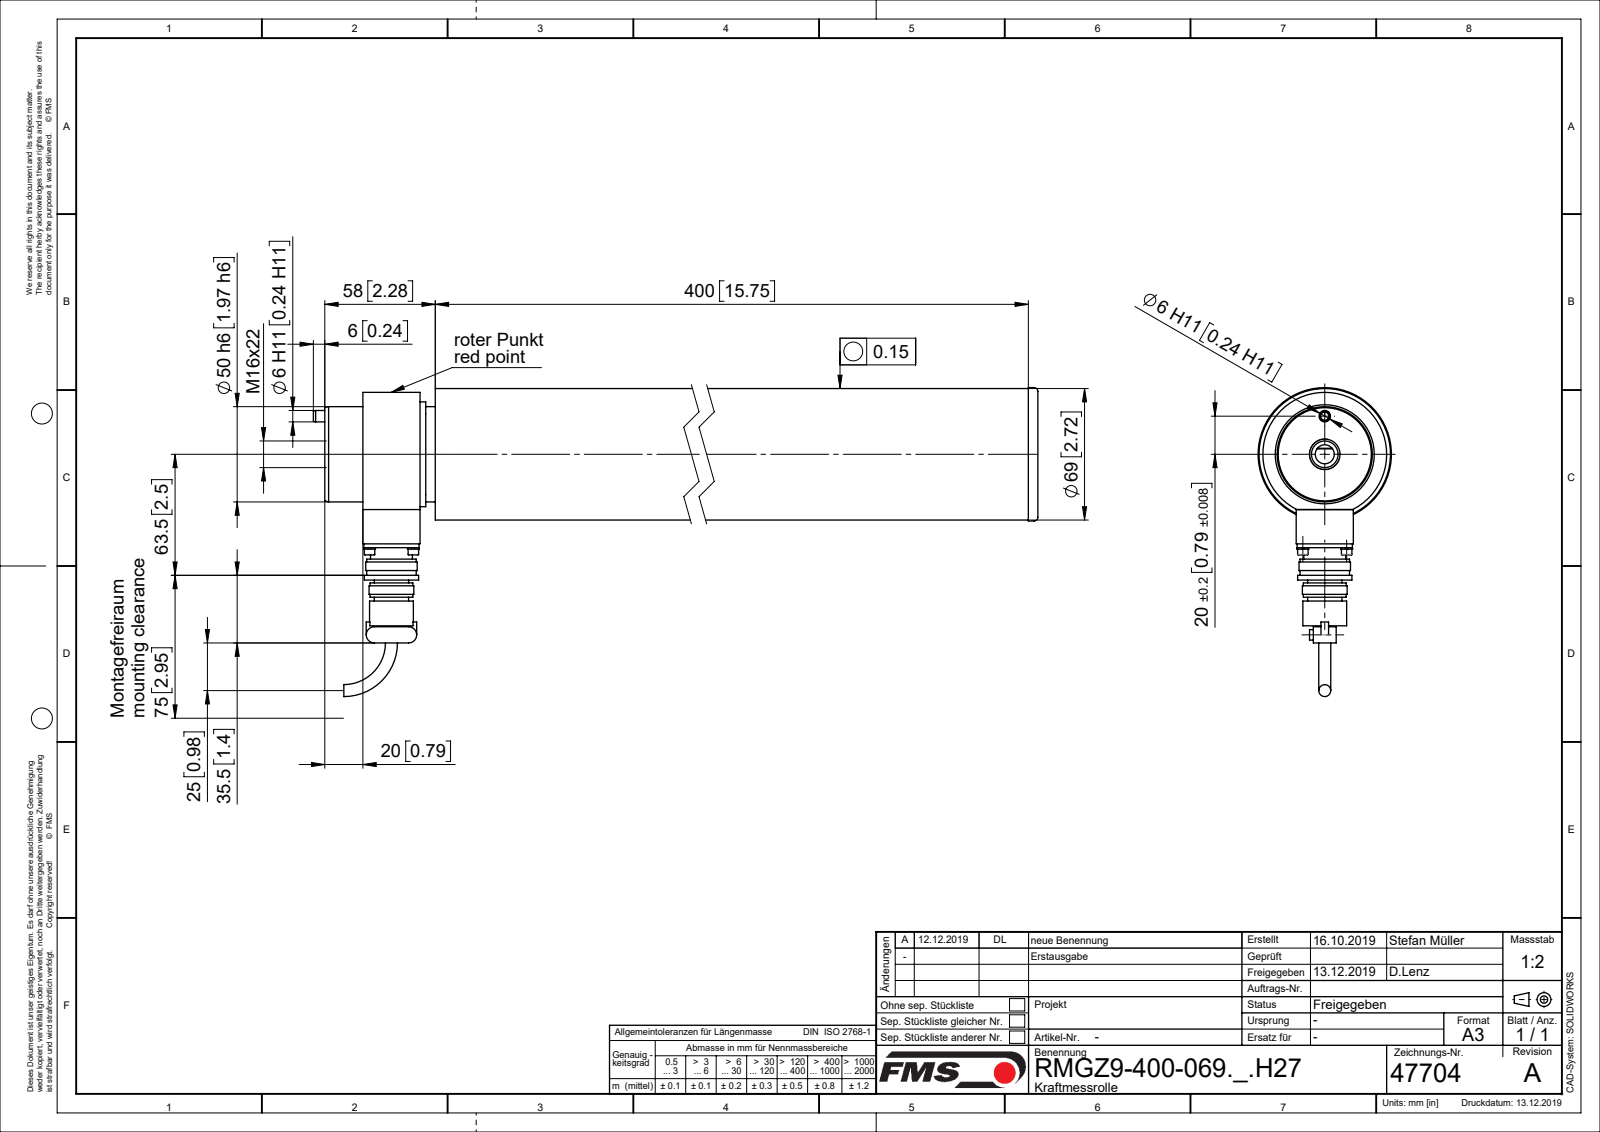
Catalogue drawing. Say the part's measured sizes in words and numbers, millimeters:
The part is named "R47704; R47708; TEIL1; R4772604 (+8 more)". Its 3-D file was written by "Mechanical Desktop 2007 (CONFIG_CONTROL_DESIGN)". It is 19 solids with 441 faces: 136 planar, 207 cylindrical and 98 other. Overall it measures 463 by 162.15 by 70 millimeters. Its volume is 880 703 cubic millimeters and its surface area 317 431 square millimeters. Round holes: 4 of diameter 2.3, 4 of diameter 3.2, 4 of diameter 3.4, 1 of diameter 10, 1 of diameter 12, 1 of diameter 13, 1 of diameter 16, 1 of diameter 17, 1 of diameter 21, 1 of diameter 23, 1 of diameter 25, 1 of diameter 26. Round bosses or shafts: 6 of diameter 5.5, 4 of diameter 6.2, 4 of diameter 3, 4 of diameter 2.5, 1 of diameter 70, 1 of diameter 69, 1 of diameter 65, 1 of diameter 59. Partial cylindrical surfaces (rounded edges, fillets, slot ends): 2 of radius 4.25, 1 of radius 17.5. The main face-to-face distances are 50, 35, 2.5, 5, 290, 115, 410, 3, 405, 13. The hole center spacings are 16.26, 23, 32.53.
